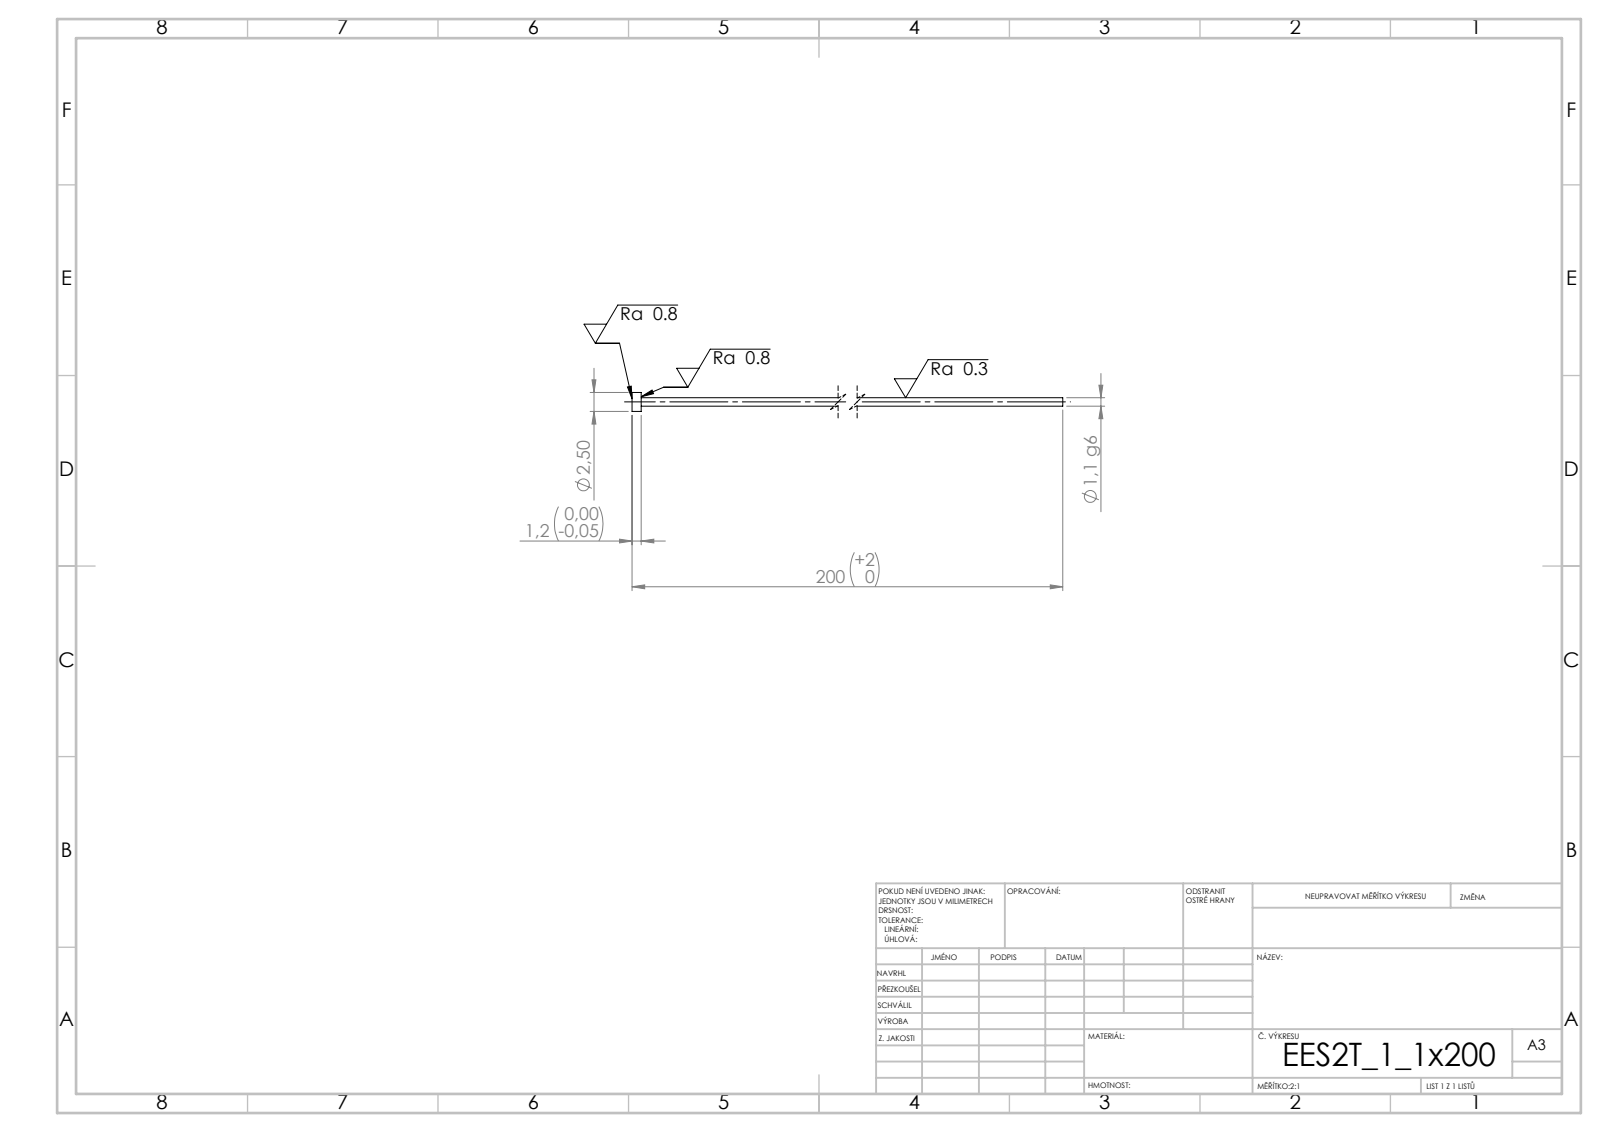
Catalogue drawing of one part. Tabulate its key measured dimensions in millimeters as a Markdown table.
| quantity | value |
| --- | --- |
| STEP written by | SolidWorks 2019 (CONFIG_CONTROL_DESIGN) |
| units | millimeters |
| bodies | 1 solid, 7 faces (3 planar, 4 cylindrical, 0 other) |
| overall size | 200 × 2.5 × 2.5 |
| volume | 195 mm³ |
| surface area | 706 mm² |
| round bosses / shafts (diameter × count) | 2.5 × 1, 1.1 × 1 |
| main face-to-face distances | 1.2, 200, 198.8 |
